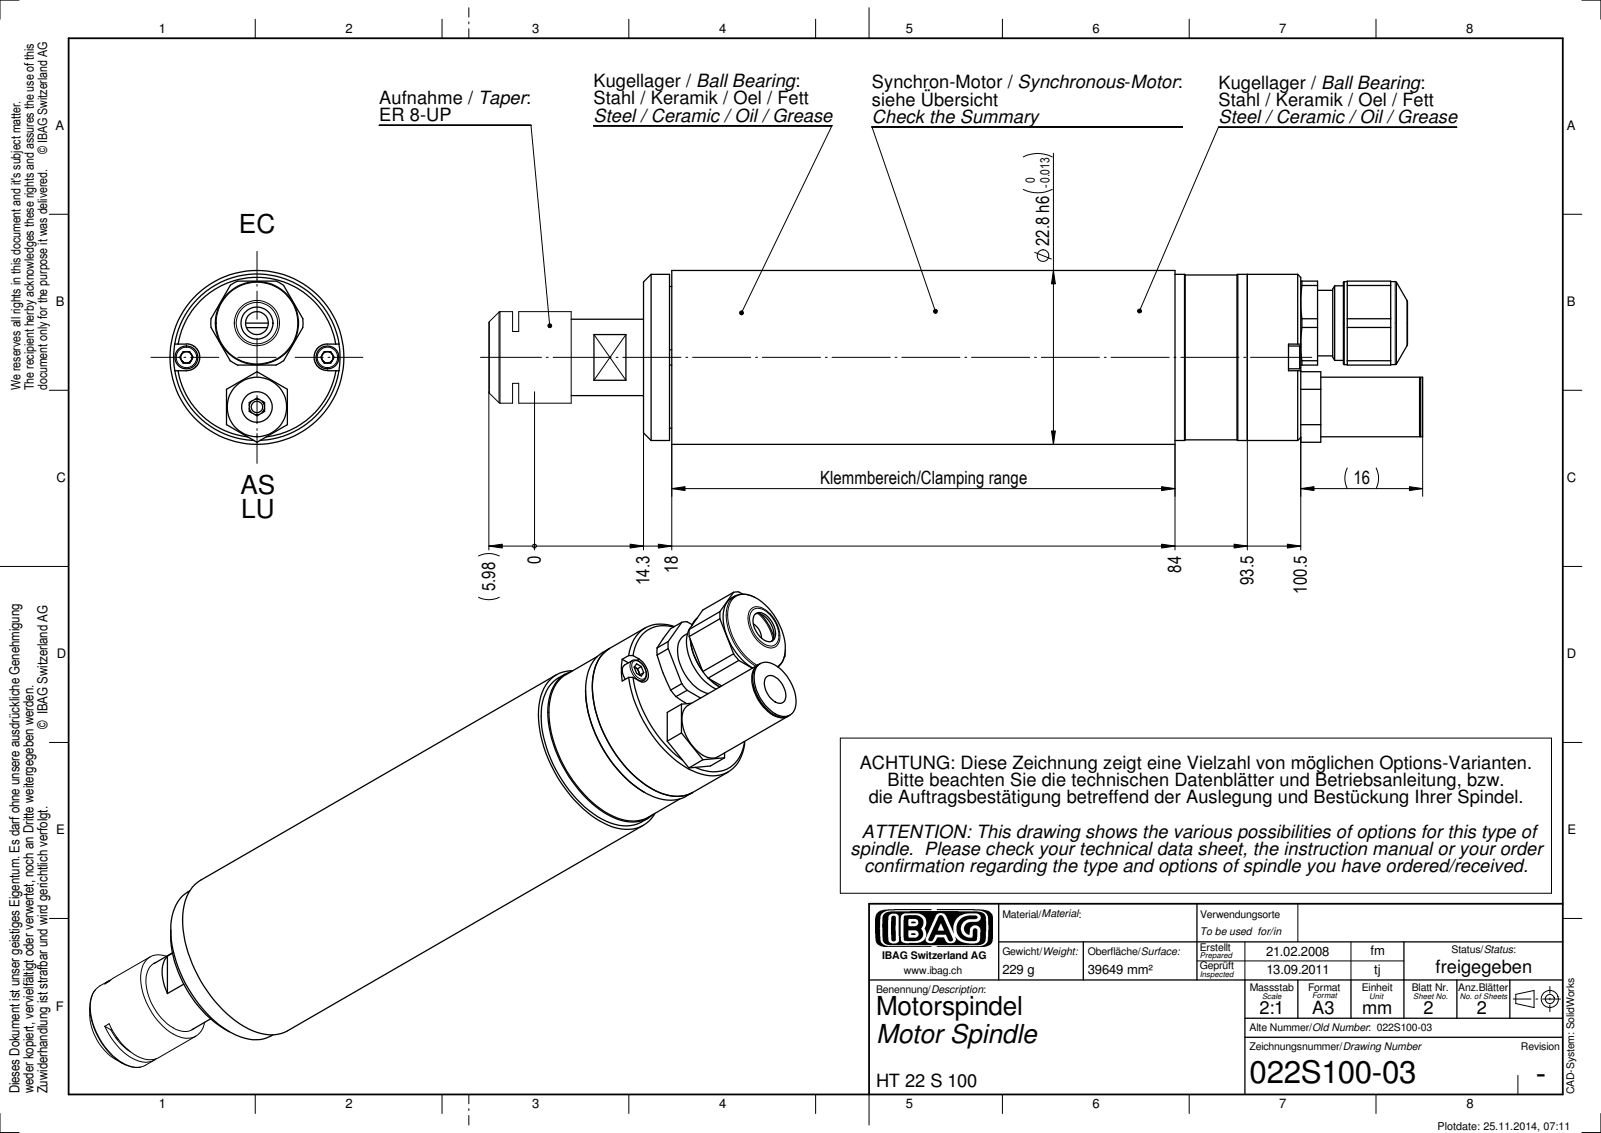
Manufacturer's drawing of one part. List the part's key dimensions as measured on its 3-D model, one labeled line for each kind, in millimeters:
Part name (STEP PRODUCT): 022S100-03
STEP written by: SolidWorks 2010 (CONFIG_CONTROL_DESIGN)
Units: millimetres
Bodies: 0 solids, 214 faces (96 planar, 73 cylindrical, 45 other)
Overall size (bounding box): 122.48 × 22.8 × 22.8
Round holes (diameter × count): ⌀1.6 ×4, ⌀3 ×2, ⌀4 ×1, ⌀4.2 ×1, ⌀5.2 ×1, ⌀9.15 ×1
Round bosses / shafts (diameter × count): ⌀3 ×2, ⌀22.8 ×1, ⌀21.8 ×1, ⌀21.6 ×1, ⌀12 ×1, ⌀10.9 ×1, ⌀10 ×1, ⌀9.79 ×1
Partial cylindrical surfaces — rounded edges, fillets, slot ends (radius × count): R1.75 ×2, R4.25 ×1, R6.05 ×1
Main face-to-face distances: 7, 79.2, 86.2, 69.7, 9.5, 16.5, 11, 3.7, 66, 75.5
Hole centre spacings: 6.5, 9.19, 7.91, 13, 2, 4.5, 11
